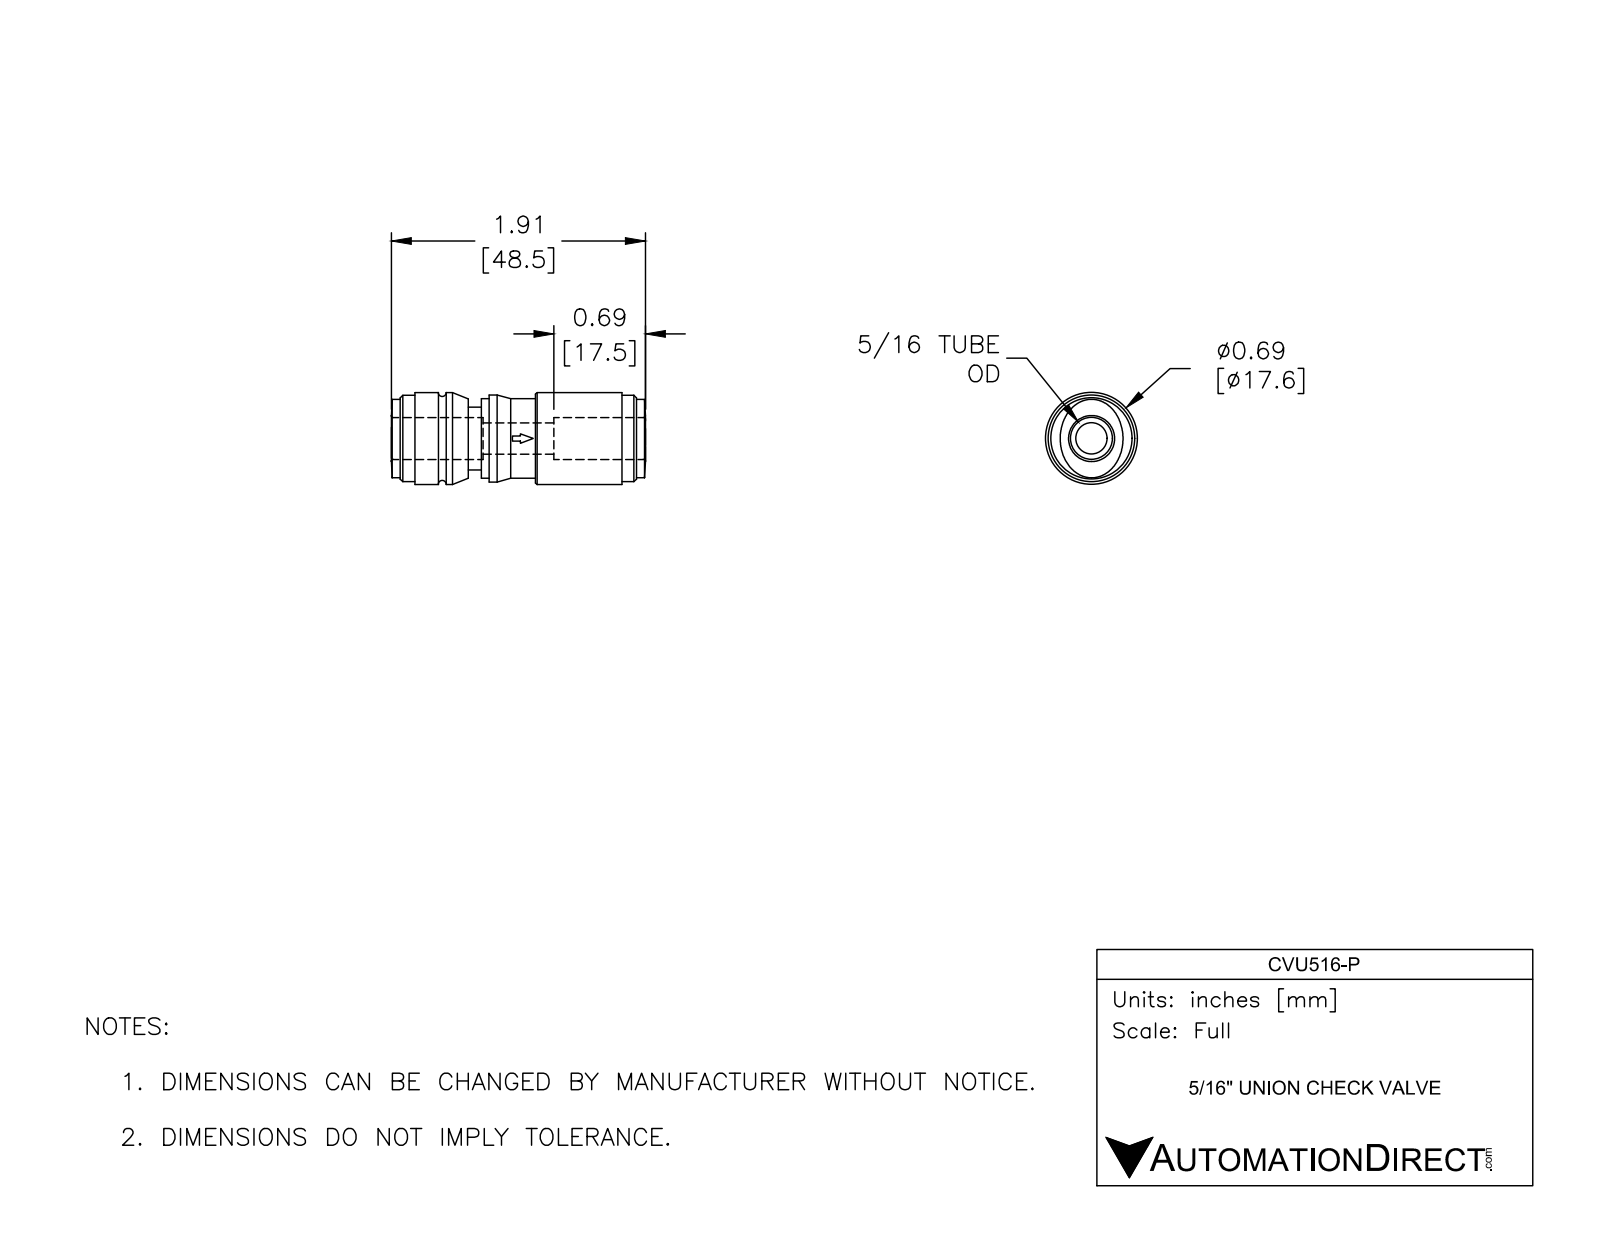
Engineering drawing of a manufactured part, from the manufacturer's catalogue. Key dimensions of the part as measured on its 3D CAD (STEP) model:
Part name (STEP PRODUCT): CVU516-P
STEP written by: SolidWorks 2017 (AUTOMOTIVE_DESIGN)
Units: inches
Bodies: 1 solid, 68 faces (17 planar, 25 cylindrical, 26 other)
Overall size (bounding box): 1.911 × 0.693 × 0.693
Volume: 0.495 in³ · Surface area: 6.654 in²
Round holes (diameter × count): ⌀0.236 ×1, ⌀0.315 ×1
Round bosses / shafts (diameter × count): ⌀0.693 ×1, ⌀0.654 ×1, ⌀0.65 ×1, ⌀0.598 ×1, ⌀0.472 ×1
Partial cylindrical surfaces — rounded edges, fillets, slot ends (radius × count): R0.303 ×1
Main face-to-face distances: 0.098, 0.11, 1.667, 0.61, 0.511, 1.167, 1.266, 1.777, 0.759, 0.408
